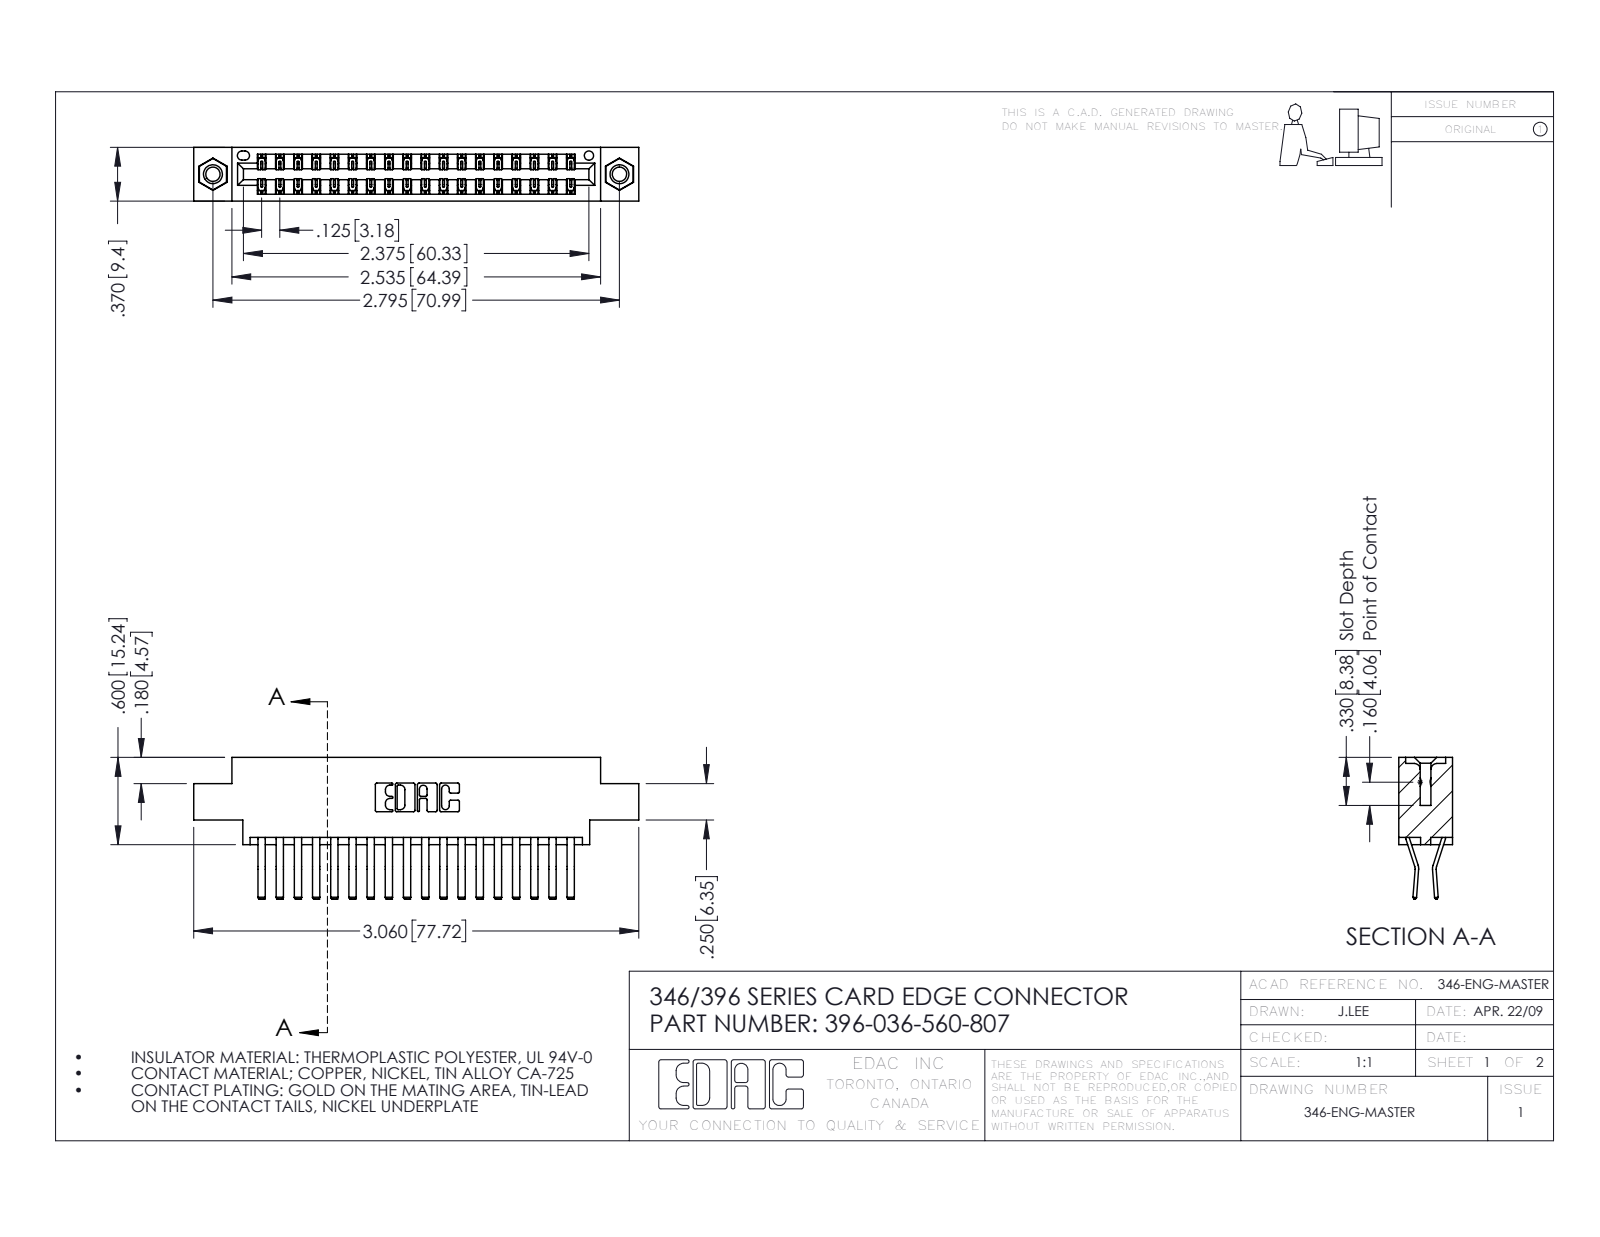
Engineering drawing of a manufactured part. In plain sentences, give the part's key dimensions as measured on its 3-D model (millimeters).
The part is named "345-250-001_345-250-005-103; 345-292-001_560 Tail; 346 Part_0.170 Offset - 0.156 Dia-TI; 396-036-560-807". Its 3-D file was written by "SolidWorks 2016 (CONFIG_CONTROL_DESIGN)". It is 39 solids with 2130 faces: 1372 planar, 742 cylindrical and 16 other. Overall it measures 77.7 by 24.8 by 9.4 millimeters. Its volume is 7 460 cubic millimeters and its surface area 10 720 square millimeters. Round holes: 2 of diameter 2.5, 2 of diameter 3.2, 2 of diameter 4, 1 of diameter 1.6. Round bosses or shafts: 2 of diameter 3.9. Partial cylindrical surfaces (rounded edges, fillets, slot ends): 54 of radius 0.2, 22 of radius 0.3, 6 of radius 0.2, 6 of radius 0.8, 3 of radius 0.7, 2 of radius 0.3, 2 of radius 0.4, 2 of radius 0.6. The main face-to-face distances are 1.2, 8.2, 9.4, 6.4, 0.6, 1.8, 7.6, 7, 5.6, 3.8. The hole center spacings are 6.2, 65.7, 71.
